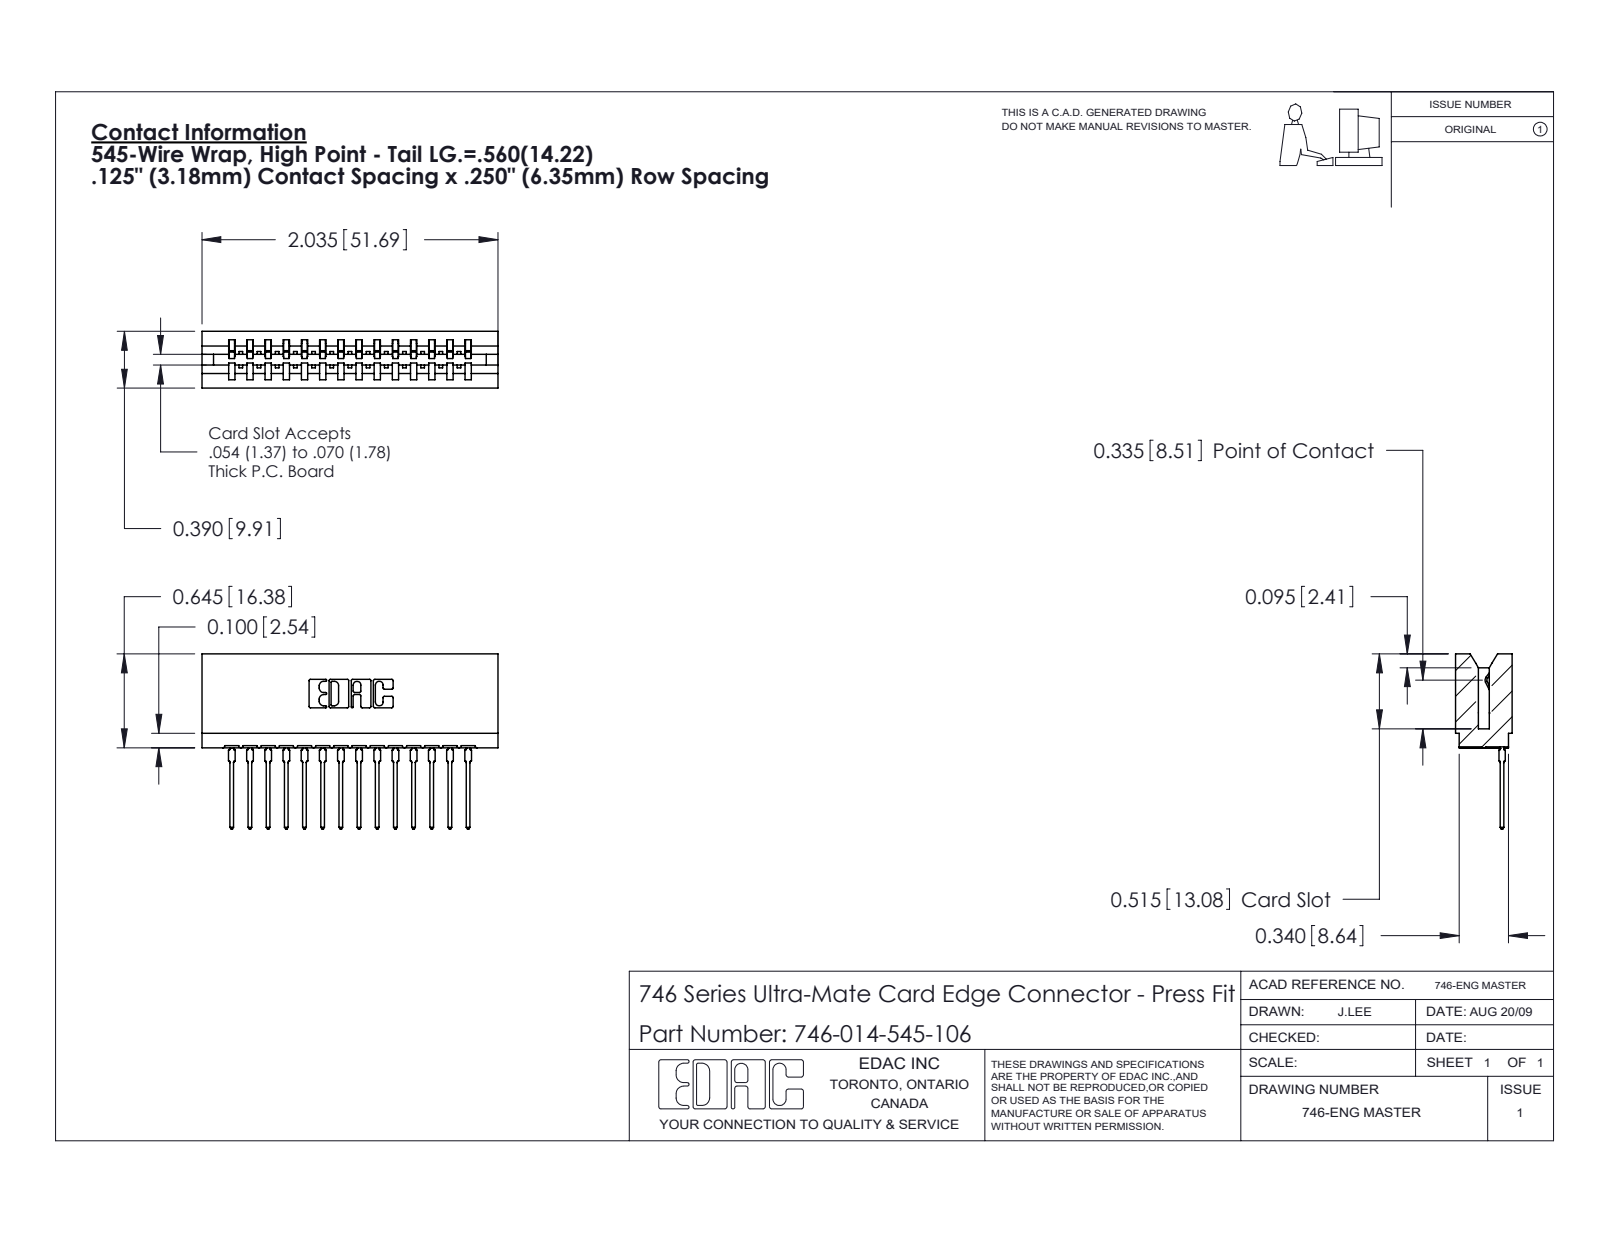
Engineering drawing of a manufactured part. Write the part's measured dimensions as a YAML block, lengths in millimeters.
part_name: "746-292-001_545; 746-014-545-106; 746 Part_.515 Slot Depth - 06"
step_written_by: "SolidWorks 2020 (CONFIG_CONTROL_DESIGN)"
units: millimeters
bodies: {solids: 15, faces: 1610, planar: 938, cylindrical: 308, other: 364}
overall_size: [51.7, 30.6, 9.9]
volume: 5600
surface_area: 8052
partial_cylinders:
  - {radius: 0.5, count: 28}
  - {radius: 0.3, count: 22}
  - {radius: 0.4, count: 15}
  - {radius: 0.2, count: 6}
  - {radius: 0.8, count: 6}
  - {radius: 0.1, count: 4}
  - {radius: 0.3, count: 4}
  - {radius: 0.7, count: 3}
face_to_face_distances: [6.4, 8.5, 1.4, 12.7, 9.9, 3.2, 2.1, 1.1, 5.3, 9.5]
